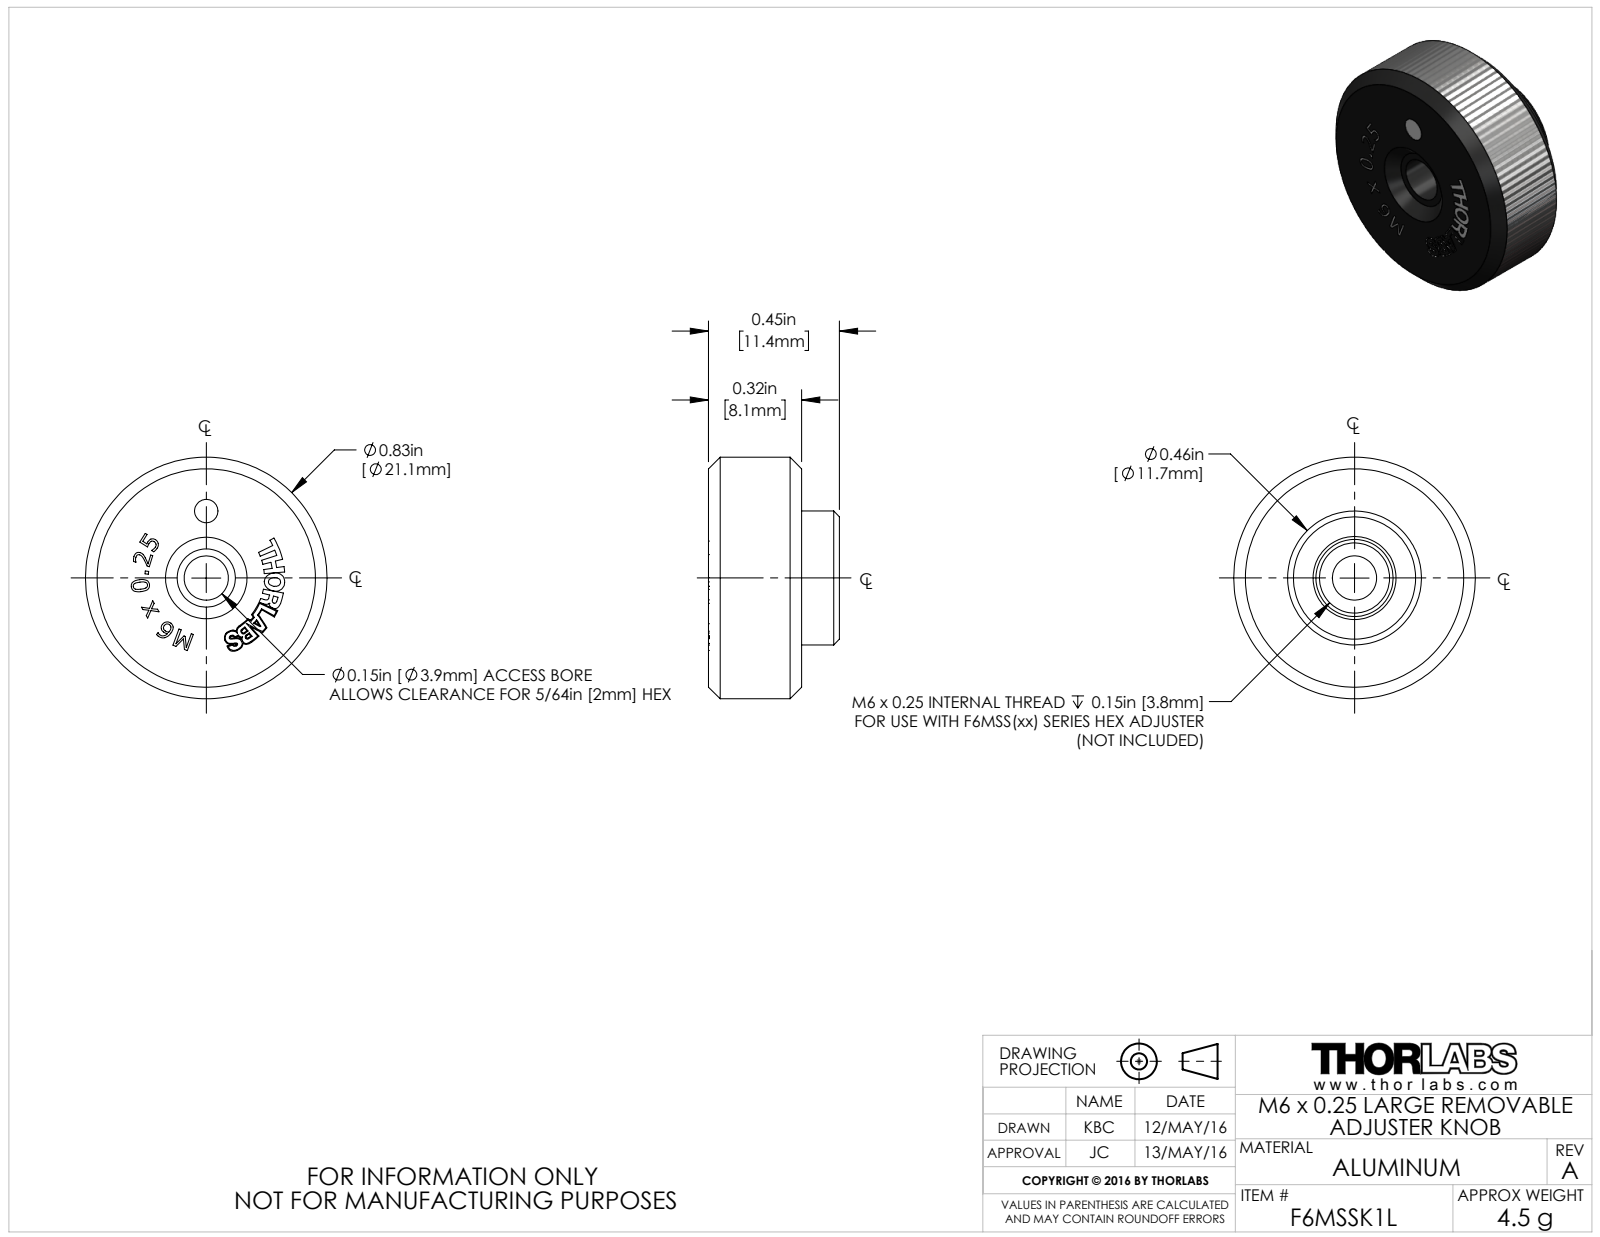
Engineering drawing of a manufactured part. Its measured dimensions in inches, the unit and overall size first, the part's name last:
Units: inches
Overall size (bounding box): 0.83 × 0.83 × 0.45
Round holes (diameter × count): ⌀0.08 ×1, ⌀0.152 ×1, ⌀0.241 ×1, ⌀0.265 ×1, ⌀0.301 ×1
Round bosses / shafts (diameter × count): ⌀0.83 ×1, ⌀0.46 ×1
Main face-to-face distances: 0.32, 0.13, 0.45, 0.18, 0.05, 0.27, 0.15, 0.02, 0.03, 0.3
Hole centre spacings: 0.23
Volume: 0.175 in³ · Surface area: 2.241 in²
Bodies: 1 solid, 297 faces (104 planar, 14 cylindrical, 179 other)
Part name (STEP PRODUCT): TTN102540-E0W
STEP written by: SolidWorks 2016 (CONFIG_CONTROL_DESIGN)
